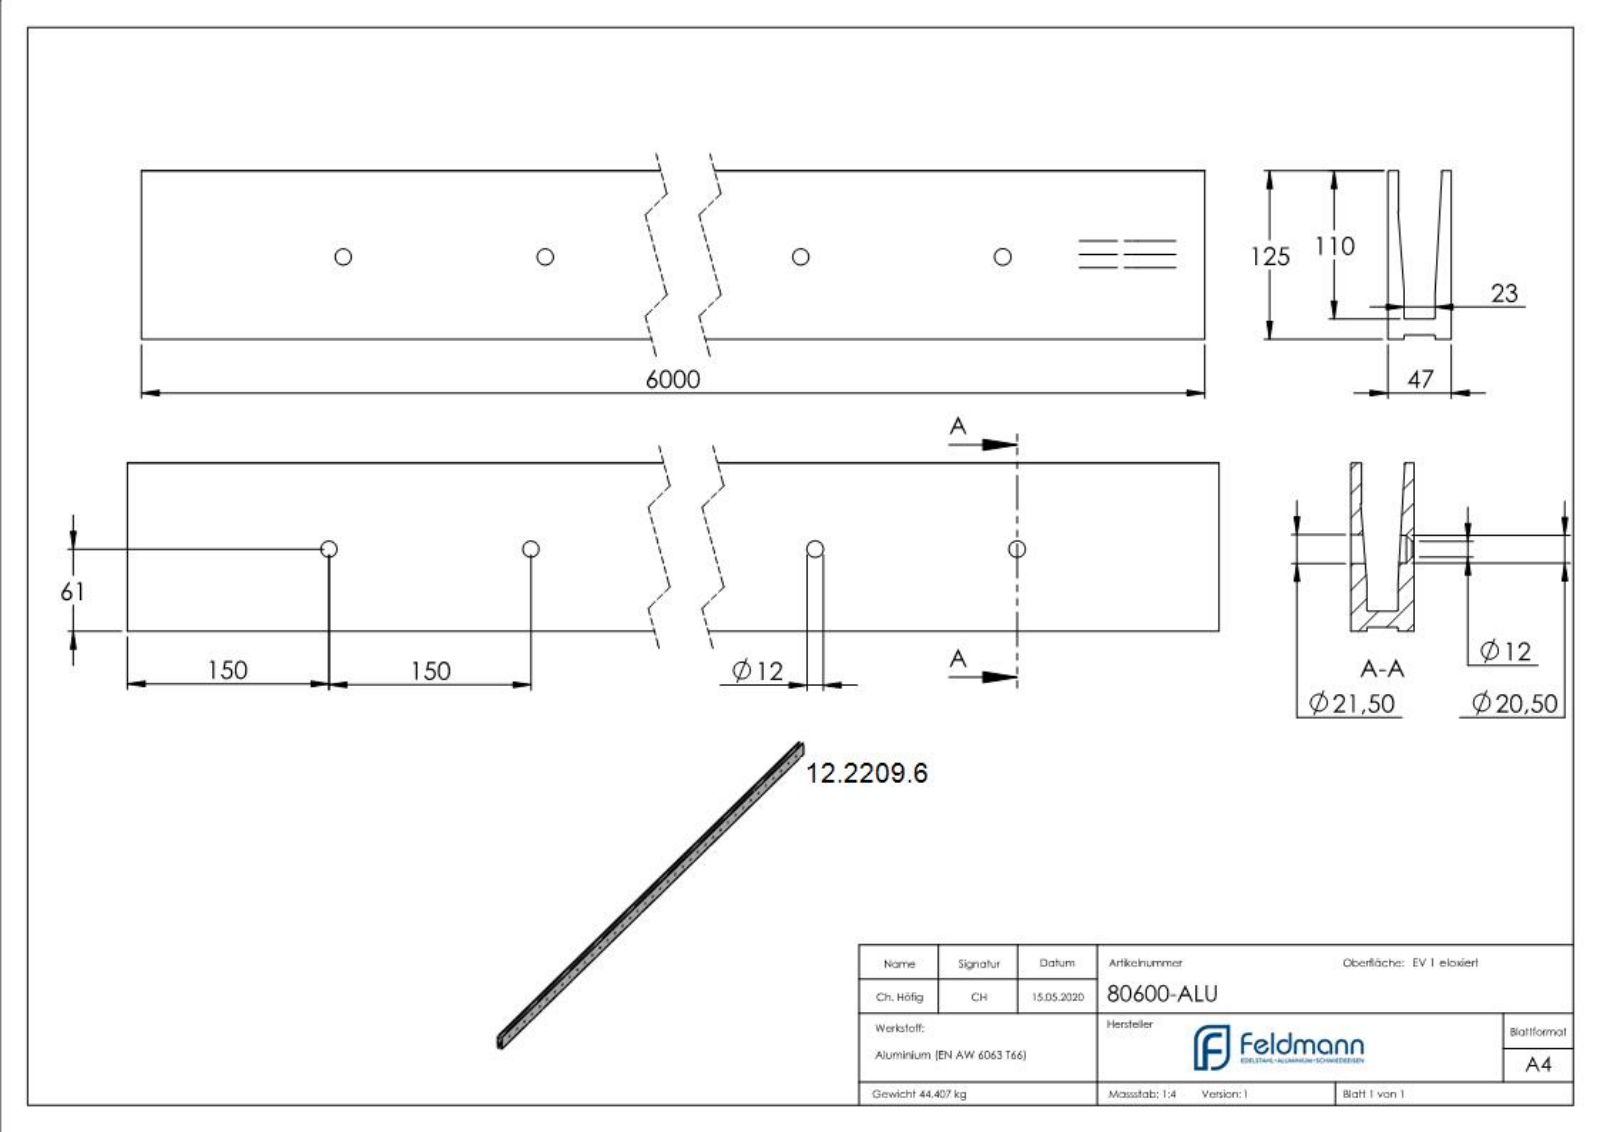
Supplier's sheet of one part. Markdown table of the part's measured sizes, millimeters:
| quantity | value |
| --- | --- |
| part name | 80600-ALU |
| STEP written by | SolidWorks 2015 (CONFIG_CONTROL_DESIGN) |
| units | millimeters |
| bodies | 1 solid, 560 faces (129 planar, 245 cylindrical, 186 other) |
| overall size | 6000 × 125 × 47 |
| volume | 16 450 000 mm³ |
| surface area | 3 371 000 mm² |
| round holes (diameter × count) | 12 × 39, 20.5 × 39, 21.5 × 39 |
| partial cylindrical surfaces (radius × count) | 0.5 × 4, 1 × 3, 0.65 × 2, 0.25 × 1 |
| main face-to-face distances | 47, 12, 35, 7.94, 39.06, 3, 4.06, 27.06, 23, 15 |
| hole center spacings | 150, 300, 450, 600, 750, 900, 1050, 1200 |
